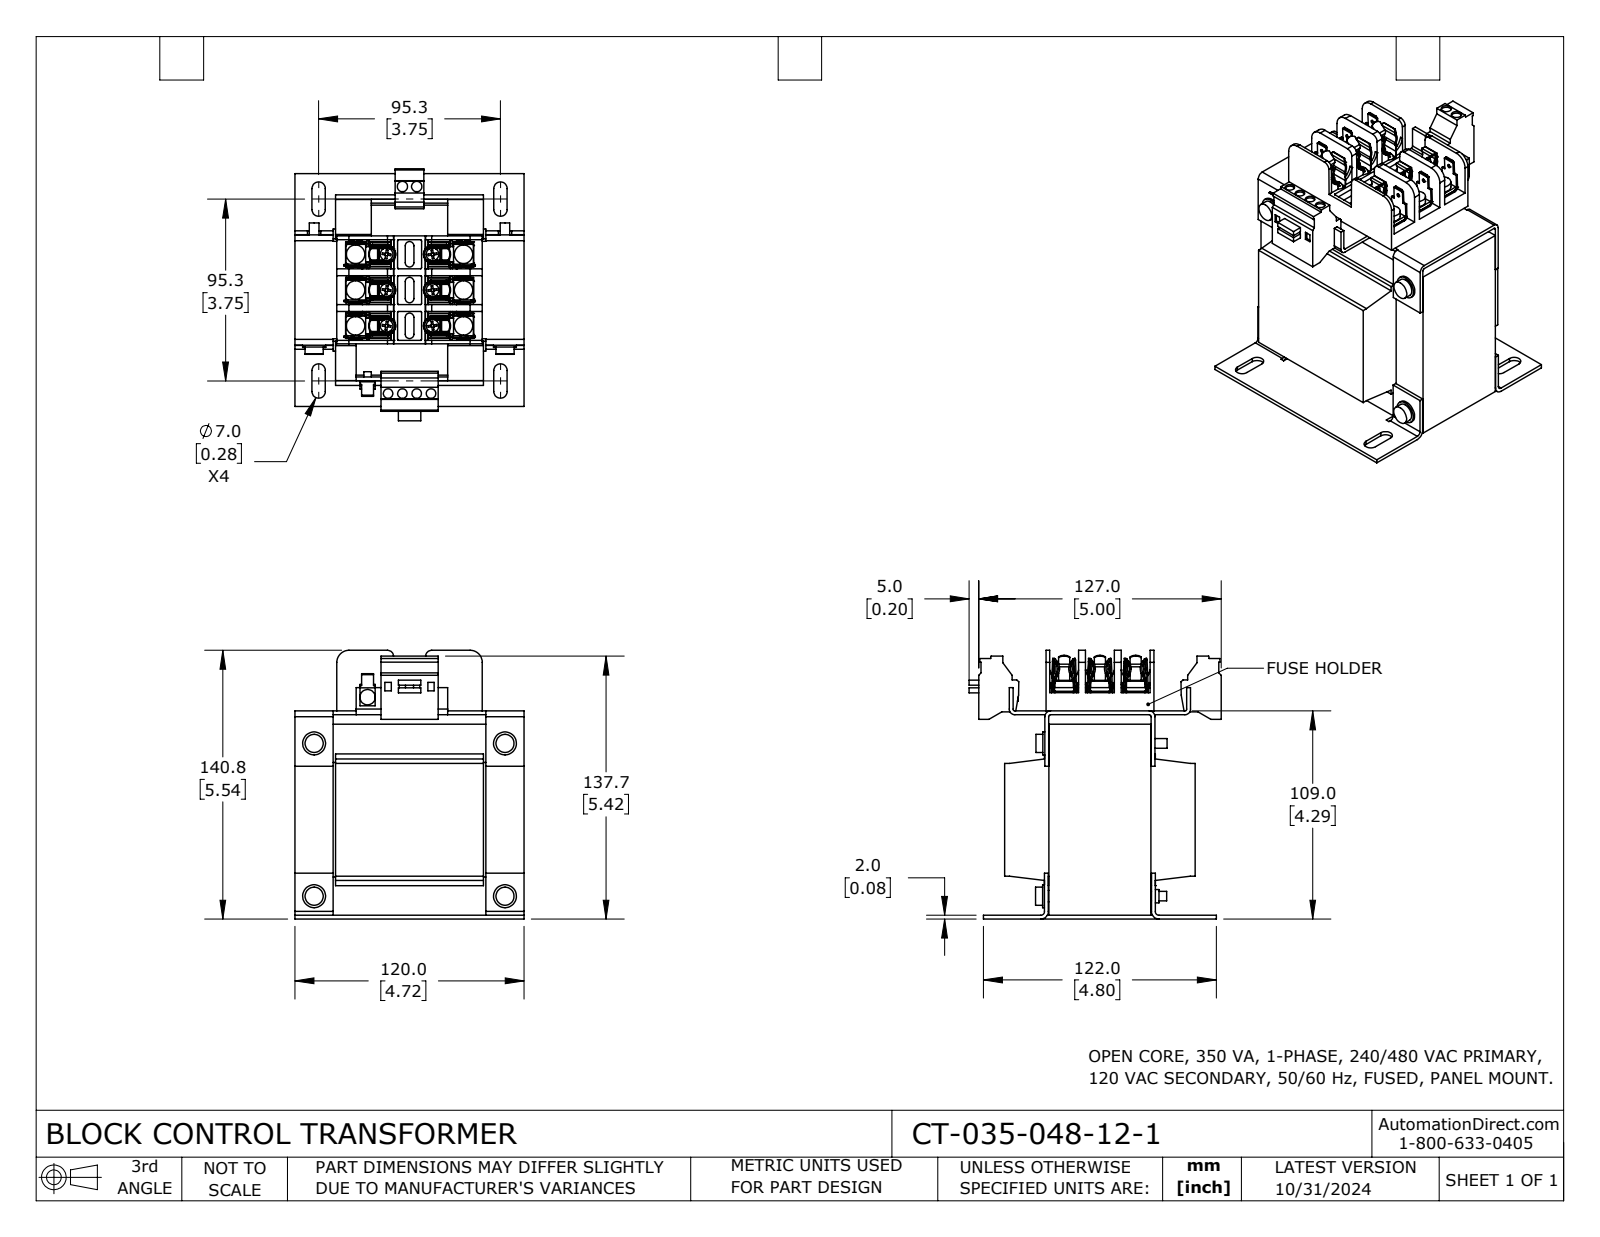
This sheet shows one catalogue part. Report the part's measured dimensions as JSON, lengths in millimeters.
{"part_name": "CT-035-048-12-1", "step_written_by": "SolidWorks 2023 (CONFIG_CONTROL_DESIGN)", "units": "millimeters", "bodies": {"solids": 2, "faces": 1588, "planar": 1027, "cylindrical": 531, "other": 30}, "overall_size": [140.7, 132, 120], "volume_mm3": 993100, "surface_area_mm2": 173200, "round_holes": [[1.9, 12], [5.2, 5], [5, 4], [5.4, 2], [5.2, 1]], "round_bosses_or_shafts": [[9.7, 6], [4.8, 6], [12, 4], [9.5, 4], [6, 4], [5, 4], [7, 2], [8, 1]], "partial_cylinders_radius": [[0.3, 24], [1.3, 20], [0.8, 18], [1.8, 14], [1, 12], [1, 12], [4.2, 12], [2.5, 9]], "face_to_face_distances": [2, 107, 100, 21.3, 98.8, 20, 109, 23.1, 76.7, 78.7], "hole_center_spacings": [56.7, 59.8, 0.7, 0.7, 1.3, 7.5, 18.7, 43.1]}
